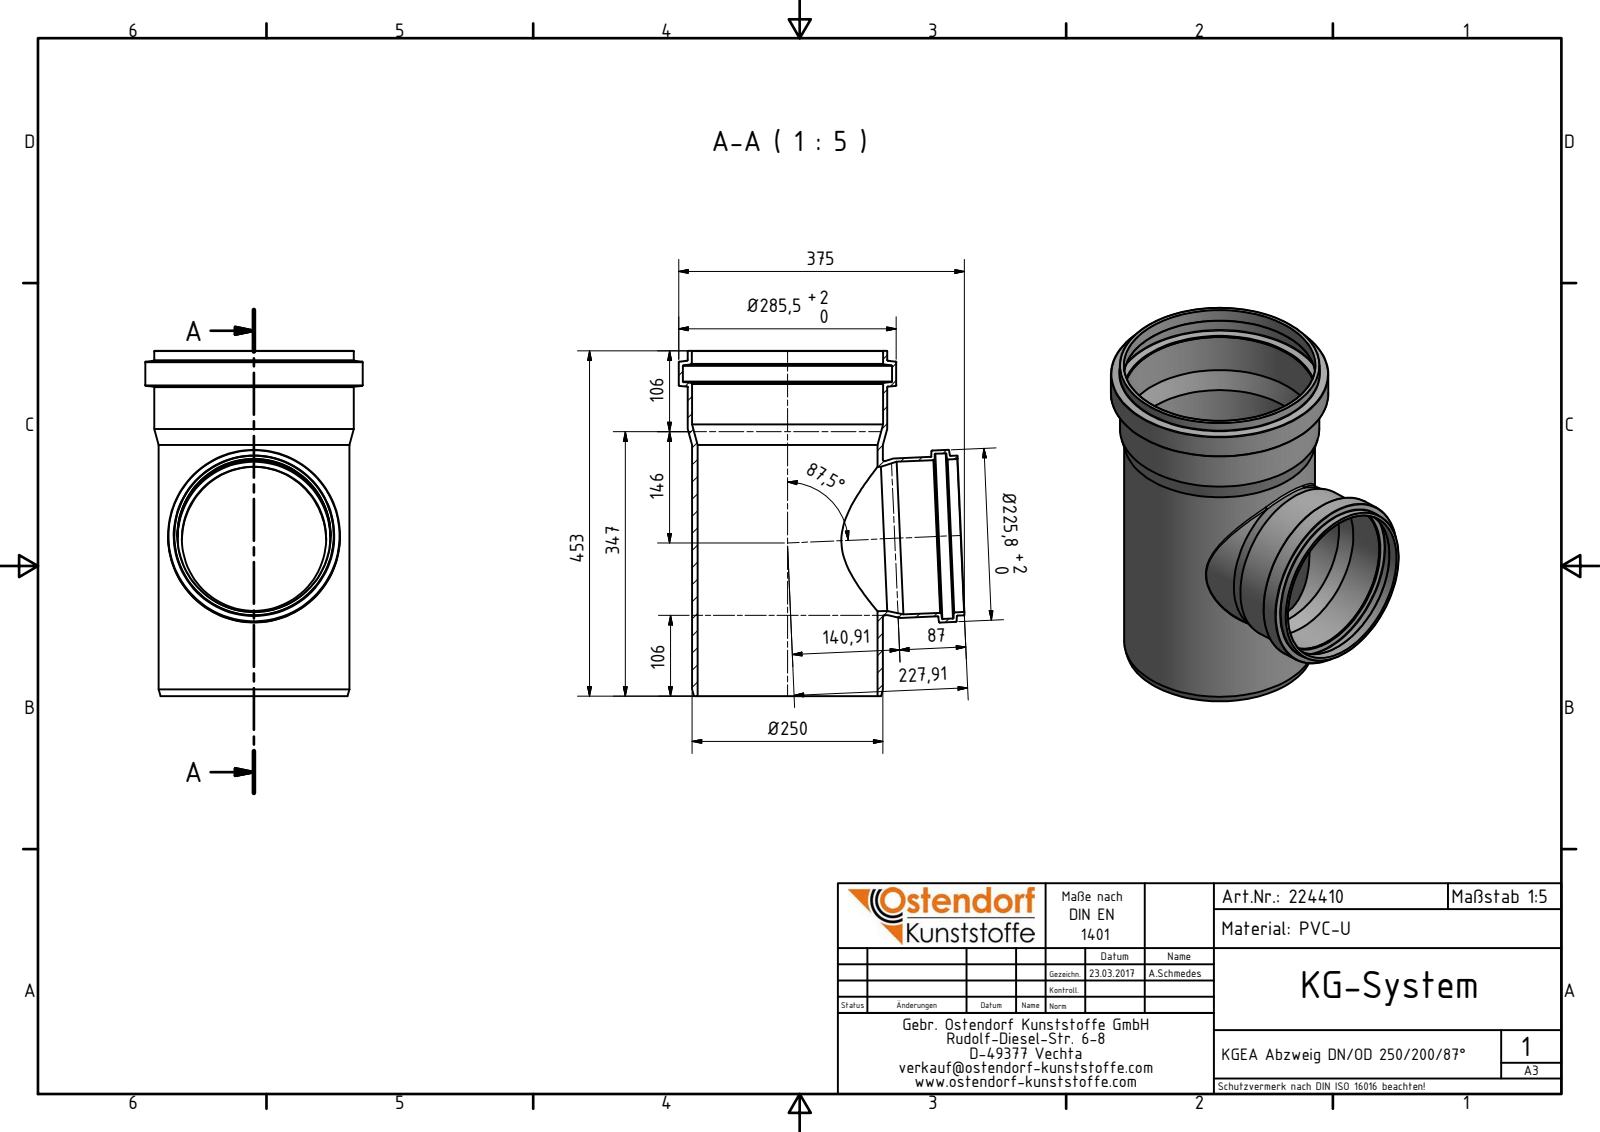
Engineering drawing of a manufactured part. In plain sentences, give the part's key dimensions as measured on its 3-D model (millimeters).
The part is named "224410 KGEA Abzweig DN_OD 250_200_87°". Its 3-D file was written by "Autodesk Inventor 2016 (AUTOMOTIVE_DESIGN)". It is 1 solid with 58 faces: 5 planar, 18 cylindrical and 35 other. Overall it measures 453 by 375 by 285.5 millimeters. Its volume is 2 671 000 cubic millimeters and its surface area 868 878 square millimeters. Round holes: 2 of diameter 200.9, 1 of diameter 189.3, 1 of diameter 200.6, 1 of diameter 217, 1 of diameter 236.3, 1 of diameter 250.8, 1 of diameter 251.1, 1 of diameter 274.5. Round bosses or shafts: 1 of diameter 285.5, 1 of diameter 262.1, 1 of diameter 261.8, 1 of diameter 250.5, 1 of diameter 225.8, 1 of diameter 209.7, 1 of diameter 209.4, 1 of diameter 200.5. The main face-to-face distances are 453, 409.77, 43.23, 31.77.
